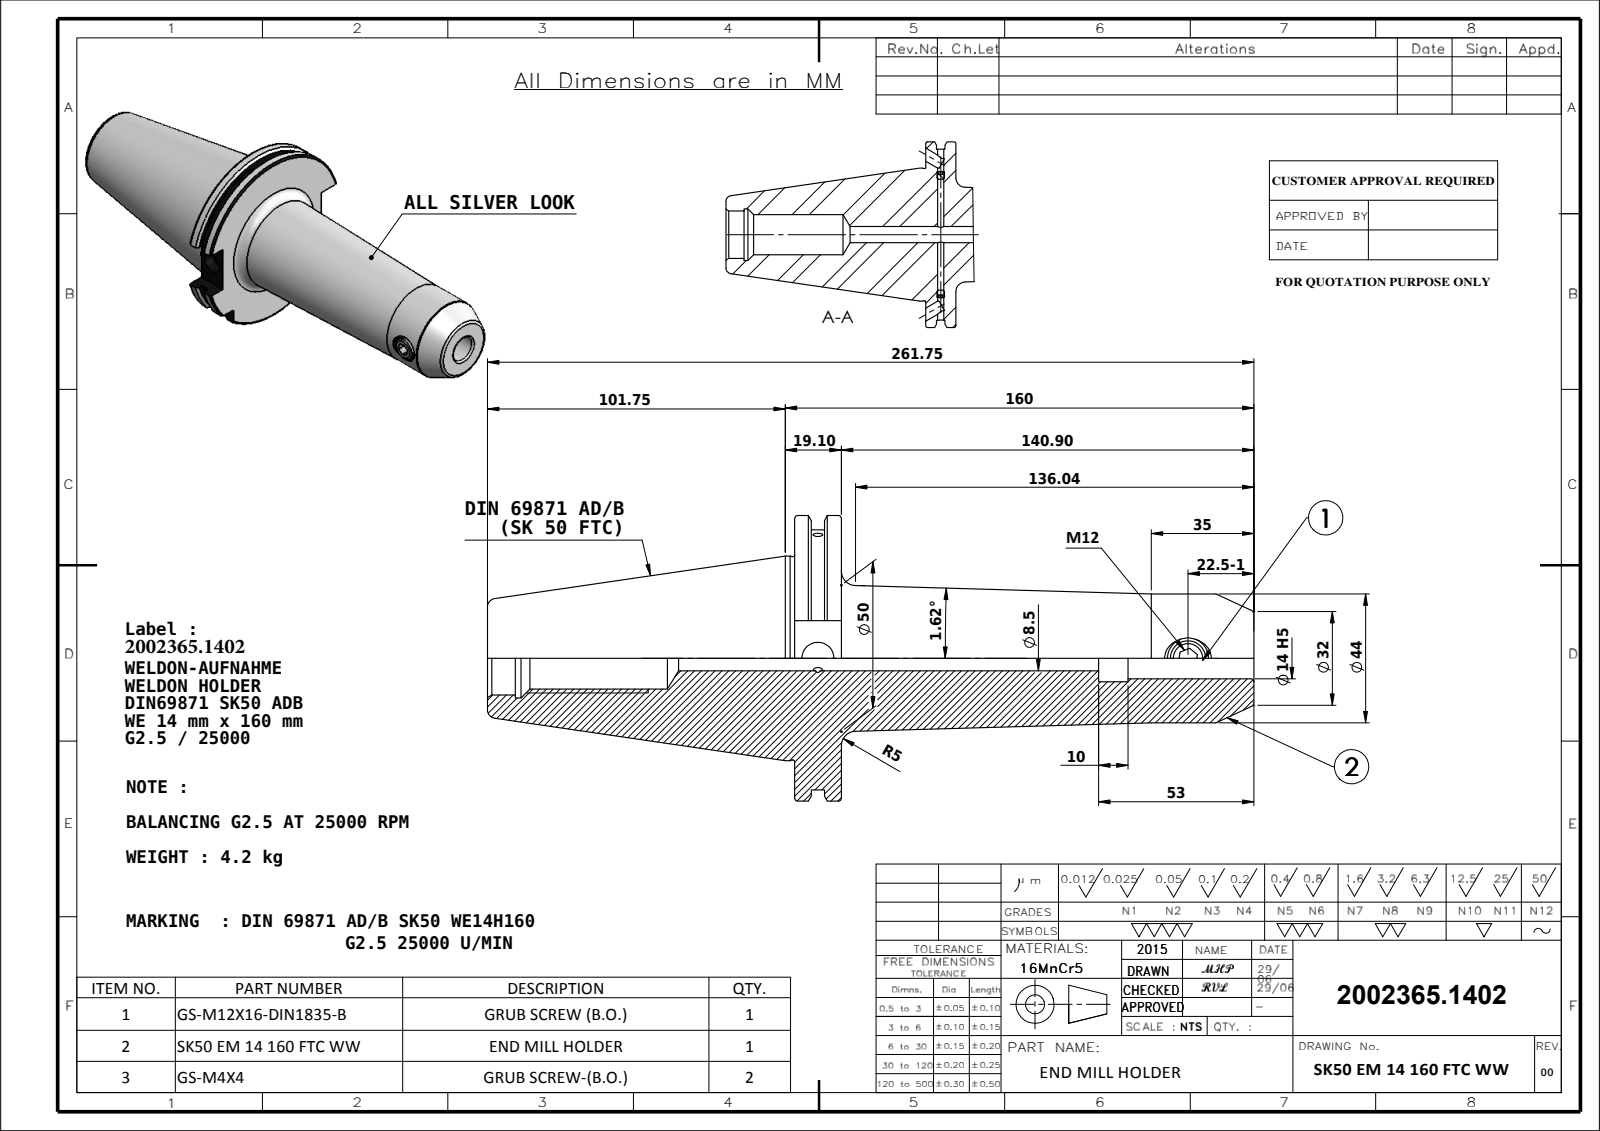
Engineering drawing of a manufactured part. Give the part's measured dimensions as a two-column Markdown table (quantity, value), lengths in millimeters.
| quantity | value |
| --- | --- |
| part name | M12X16._ISO 4026 - M12 x 12-N; M4X4_DIN 913 - M4 x 4-N; 91506-WE714160; SK50 EM 14 160 FTC WW |
| STEP written by | SolidWorks 2009 (CONFIG_CONTROL_DESIGN) |
| units | millimeters |
| bodies | 4 solids, 170 faces (53 planar, 55 cylindrical, 62 other) |
| overall size | 261.75 × 97.5 × 94.05 |
| volume | 553 735 mm³ |
| surface area | 68 310 mm² |
| round holes (diameter × count) | 6 × 2, 14 × 2, 3.3 × 1, 8.5 × 1, 10.2 × 1, 11 × 1, 16 × 1, 21 × 1, 25 × 1, 27 × 1 |
| round bosses / shafts (diameter × count) | 4 × 2, 69.85 × 1, 69.45 × 1, 44 × 1, 12 × 1 |
| partial cylindrical surfaces (radius × count) | 44.9 × 1, 48.75 × 1 |
| main face-to-face distances | 15.9, 5.66, 10.24, 10.15, 4.49, 5.75, 156.8, 151.14, 146.65, 140.9 |
| hole center spacings | 126.4 |
